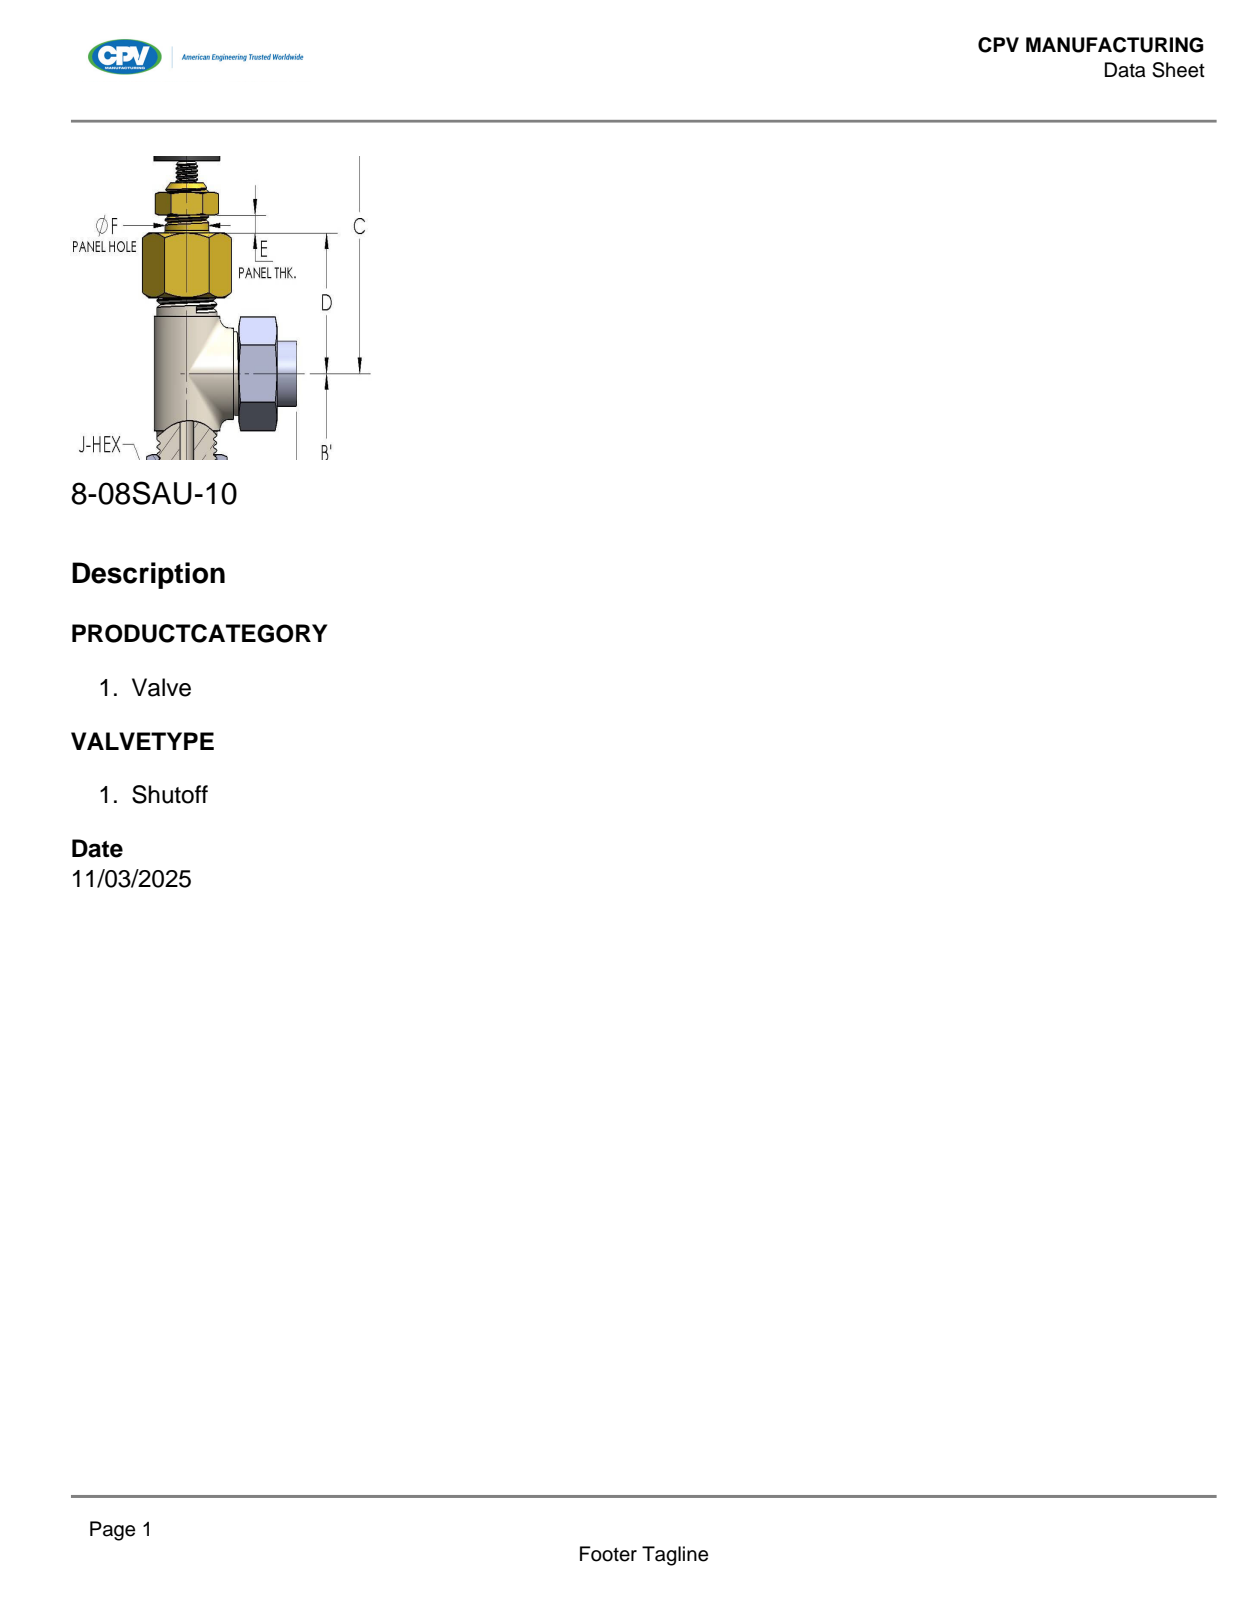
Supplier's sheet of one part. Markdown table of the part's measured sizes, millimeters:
| quantity | value |
| --- | --- |
| part name | 8-08SAU-10 |
| STEP written by | SolidWorks 2018 (AUTOMOTIVE_DESIGN) |
| units | millimeters |
| bodies | 1 solid, 181 faces (60 planar, 49 cylindrical, 72 other) |
| overall size | 127.6 × 70.1 × 47.8 |
| volume | 97 080 mm³ |
| surface area | 24 900 mm² |
| round holes (diameter × count) | 13.9 × 2, 16 × 2, 6.4 × 1, 7.5 × 1 |
| round bosses / shafts (diameter × count) | 25.3 × 2, 20.7 × 2, 47.8 × 1, 25.4 × 1, 19 × 1, 7.9 × 1, 6.4 × 1 |
| main face-to-face distances | 28.7, 28.7, 28.6, 7.9, 28.7, 20.6, 12.7, 40.1, 32.2, 19.5 |
